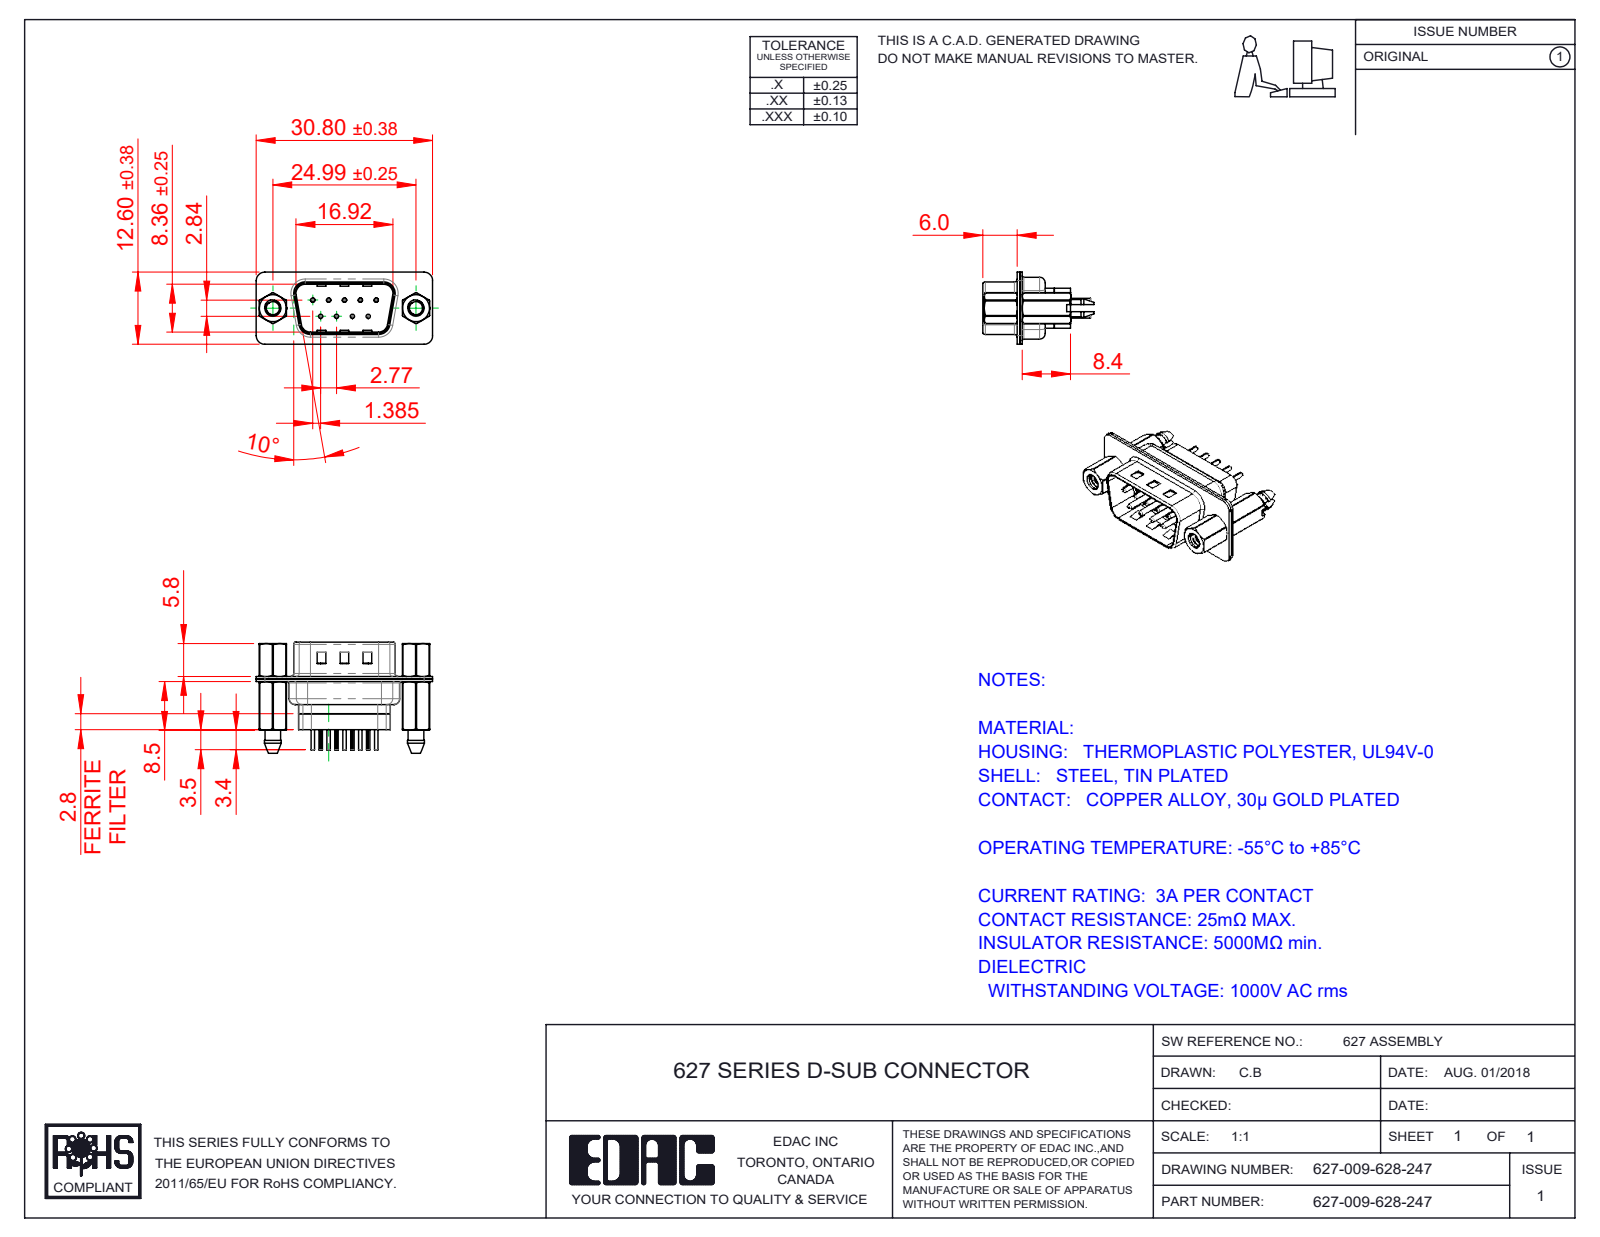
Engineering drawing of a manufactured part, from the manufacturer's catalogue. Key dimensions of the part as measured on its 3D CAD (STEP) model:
Part name (STEP PRODUCT): 627 Shell Front_09 Contacts; 627 4-40 Hex Standoff; 627 Contact Row 1_28L; 627 Shell Rear_09 Contacts (+4 more)
STEP written by: SolidWorks 2020 (CONFIG_CONTROL_DESIGN)
Units: millimetres
Bodies: 17 solids, 1497 faces (383 planar, 623 cylindrical, 491 other)
Overall size (bounding box): 30.8 × 19.4 × 12.6
Volume: 1 953 mm³ · Surface area: 5 340 mm²
Round holes (diameter × count): ⌀0.2 ×9, ⌀0.35 ×9, ⌀1.1 ×9, ⌀1.6 ×9, ⌀2.26 ×2, ⌀2.29 ×2, ⌀4 ×2, ⌀4.8 ×2
Round bosses / shafts (diameter × count): ⌀2 ×9, ⌀1.5 ×9, ⌀0.75 ×9, ⌀0.6 ×9, ⌀4.9 ×2, ⌀2.79 ×2
Partial cylindrical surfaces — rounded edges, fillets, slot ends (radius × count): R1.5 ×20, R0.1 ×18, R2 ×12, R1.6 ×10, R0.5 ×8, R0.25 ×4, R0.6 ×4, R0.65 ×4
Main face-to-face distances: 0.4, 0.45, 0.9, 6.5, 6.05, 5.6, 0.82, 9.58, 8.4, 1.4
Hole centre spacings: 3.16, 2.77, 5.54, 5.03, 5.04, 8.31, 7.48, 7.49
